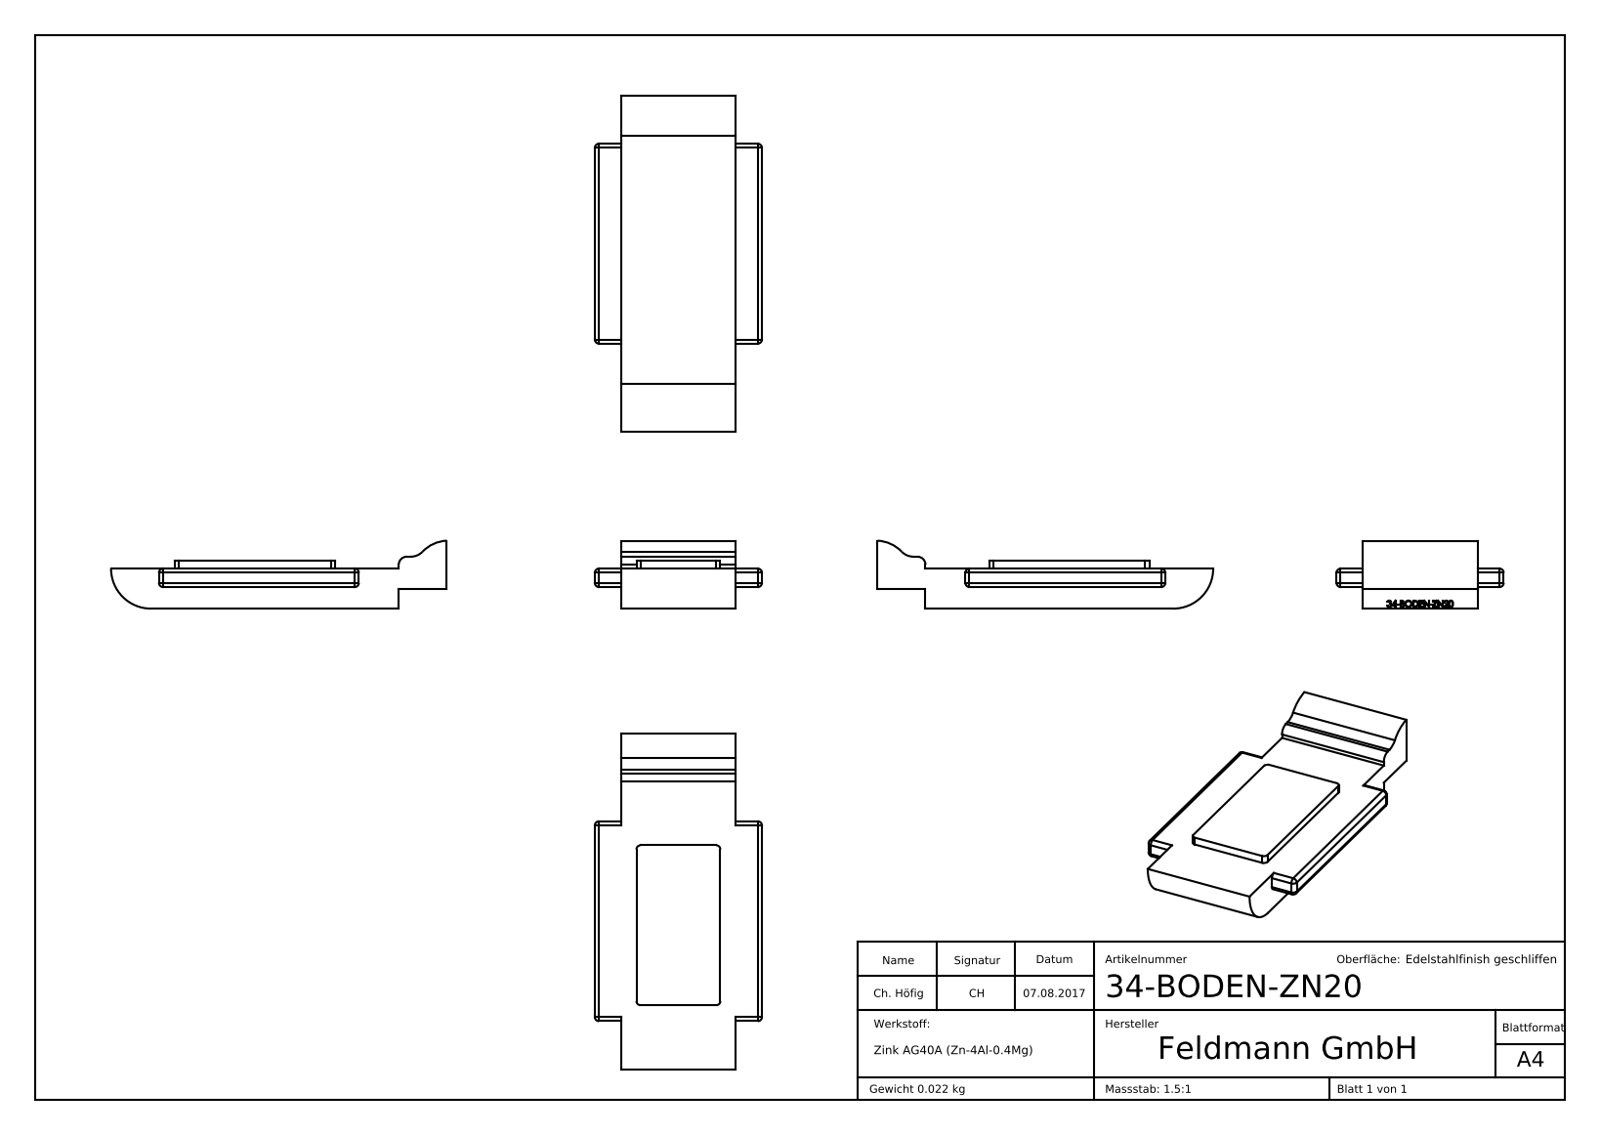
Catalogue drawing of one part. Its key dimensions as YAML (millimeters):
part_name: "34-Boden-V4A ohne Gummi_34-BODEN-ZN20; 34-BODEN-ZN20; 34-Boden Gummi_34-BODEN-XXX"
step_written_by: "SolidWorks 2015 (CONFIG_CONTROL_DESIGN)"
units: millimeters
bodies: {solids: 2, faces: 212, planar: 127, cylindrical: 24, other: 61}
overall_size: [42, 20.9, 8.5]
volume: 3505
surface_area: 2614
partial_cylinders:
  - {radius: 0.5, count: 16}
  - {radius: 1, count: 1}
  - {radius: 2, count: 1}
  - {radius: 4.5, count: 1}
  - {radius: 5, count: 1}
face_to_face_distances: [5, 6, 1, 2.5, 14.4, 2.3, 2.7, 3.3, 3.5, 3.25]
